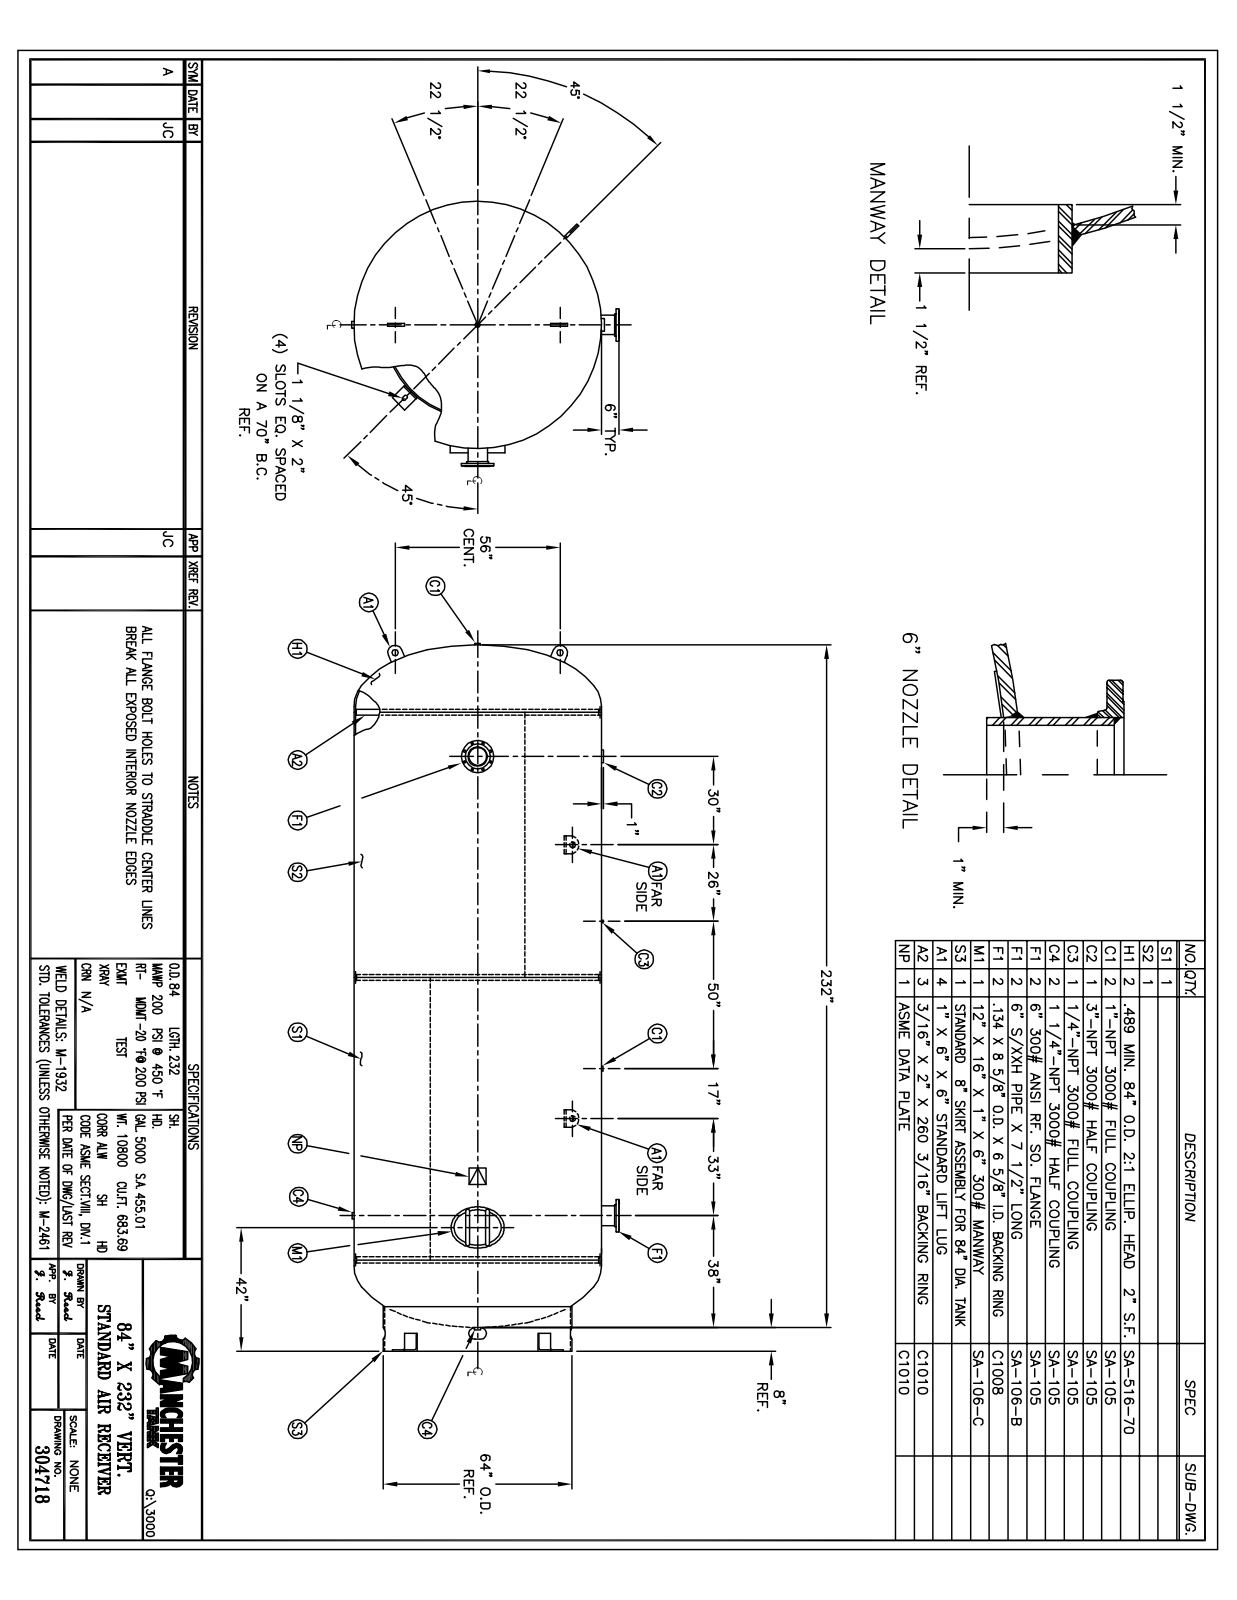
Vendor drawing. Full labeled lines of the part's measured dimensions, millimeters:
Part name (STEP PRODUCT): 304718
STEP written by: SolidWorks 2012 (CONFIG_CONTROL_DESIGN)
Units: millimetres
Bodies: 0 solids, 334 faces (118 planar, 173 cylindrical, 43 other)
Overall size (bounding box): 6125.8 × 2308.1 × 2298.7
Round holes (diameter × count): ⌀22.2 ×8, ⌀22.2 ×8, ⌀50.8 ×4, ⌀42.2 ×2, ⌀146.3 ×2, ⌀170.7 ×2, ⌀13.7 ×1, ⌀33.4 ×1, ⌀88.9 ×1, ⌀171.5 ×1, ⌀1600.2 ×1, ⌀2108.2 ×1
Round bosses / shafts (diameter × count): ⌀279.4 ×2, ⌀215.9 ×2, ⌀57.2 ×2, ⌀25.4 ×2, ⌀2133.6 ×1, ⌀1625.6 ×1, ⌀168.3 ×1, ⌀168.3 ×1
Partial cylindrical surfaces — rounded edges, fillets, slot ends (radius × count): R12.7 ×8, R14.3 ×8, R12.7 ×4, R33.5 ×4, R74.6 ×4, R74.6 ×4, R9.5 ×3, R150.3 ×1
Main face-to-face distances: 3072.6, 12.7, 2438.4, 5511, 4714.9, 2276.5, 796.1, 25.4, 5498.3, 3059.9
Hole centre spacings: 92.3, 120.7, 170.6, 222.9, 222.9, 92.4, 120.7, 170.6
